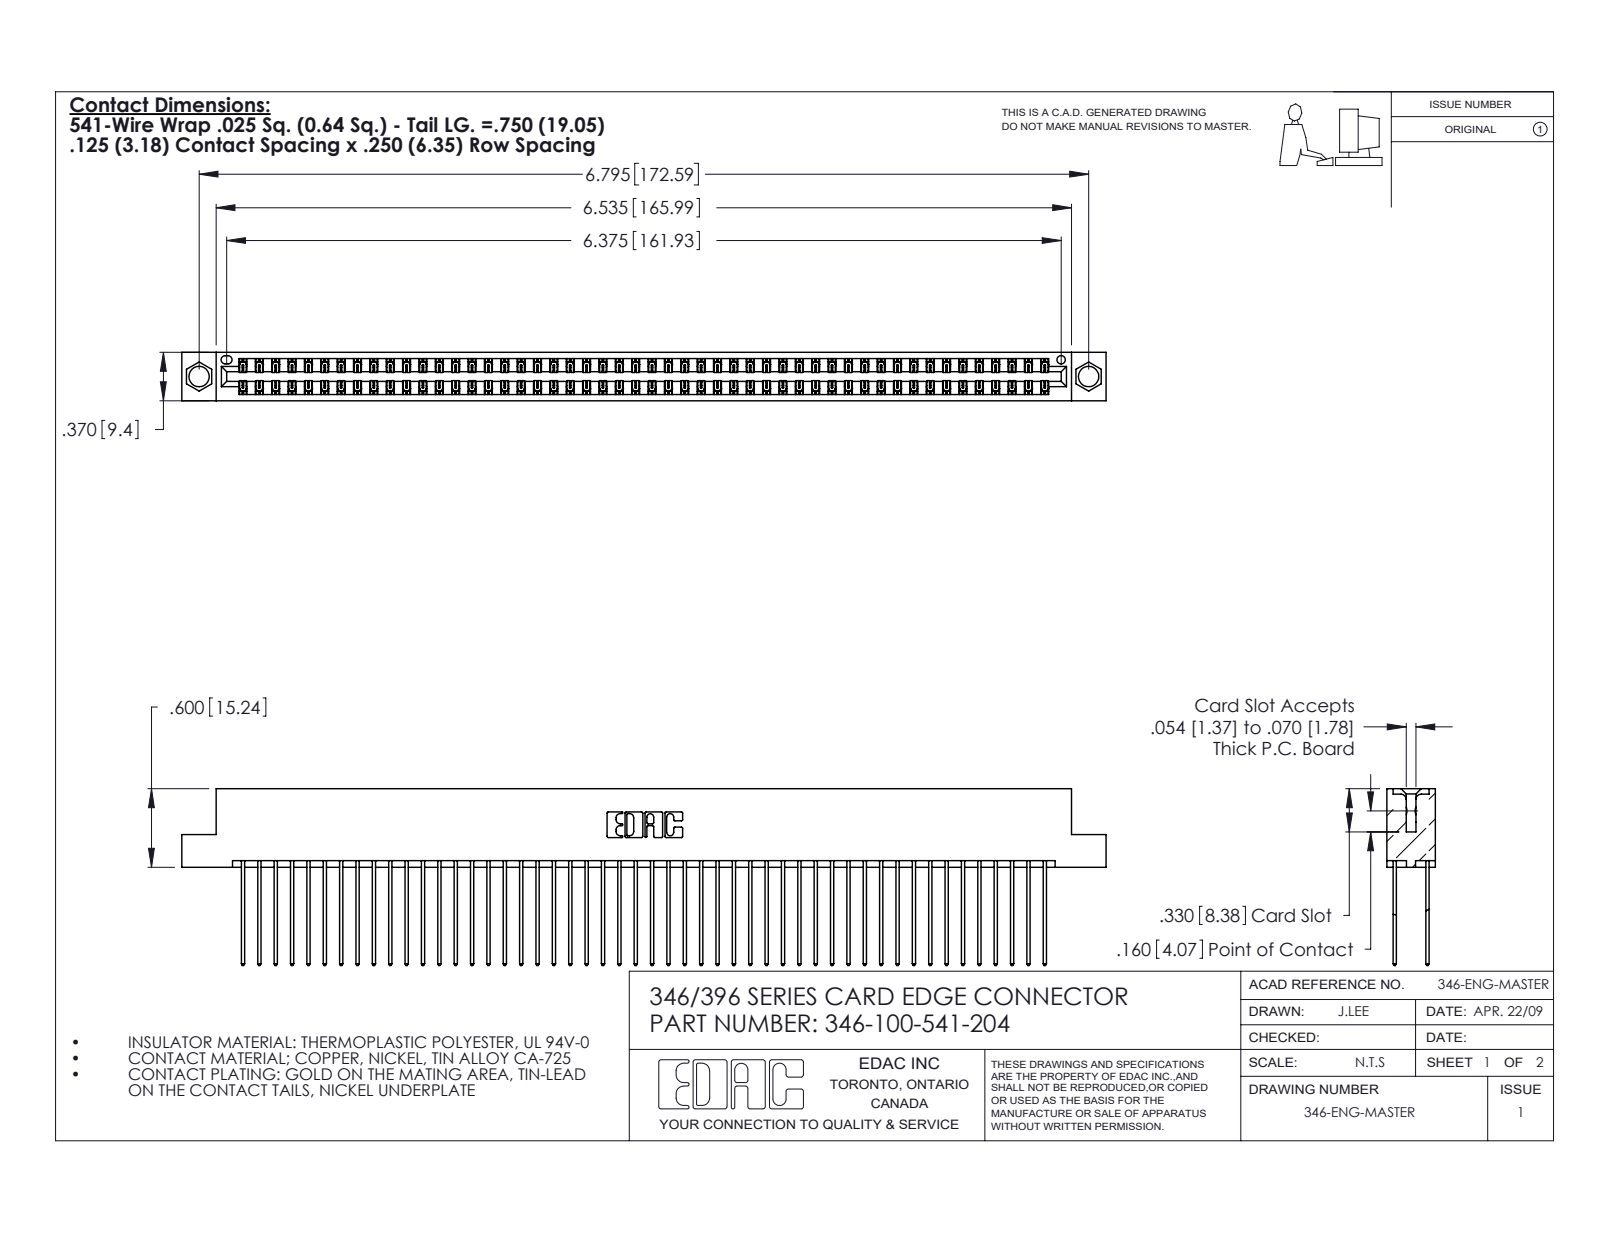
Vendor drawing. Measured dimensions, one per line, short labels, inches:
name: 346-100-541-204; 345-292-001_345-293-141; 346 Part_Flush Mounting Lugs - 0.156 Dia-TH
written by: SolidWorks 2020 (CONFIG_CONTROL_DESIGN)
unit: in
bodies: 101 solids, 5336 faces (3590 planar, 1746 cylindrical, 0 other)
size: 7.06 × 1.35 × 0.37
volume: 1.099 in³; area: 42.61 in²
holes: 2× ⌀0.156, 1× ⌀0.064
rounds: 150× R0.006, 100× R0.01, 22× R0.01, 6× R0.007, 6× R0.031, 3× R0.026, 2× R0.014, 2× R0.022
face distances: 0.048, 0.322, 0.25, 0.072, 0.298, 0.025, 0.37, 0.275, 0.225, 0.148
hole spacings: 0.246, 6.586, 6.795
